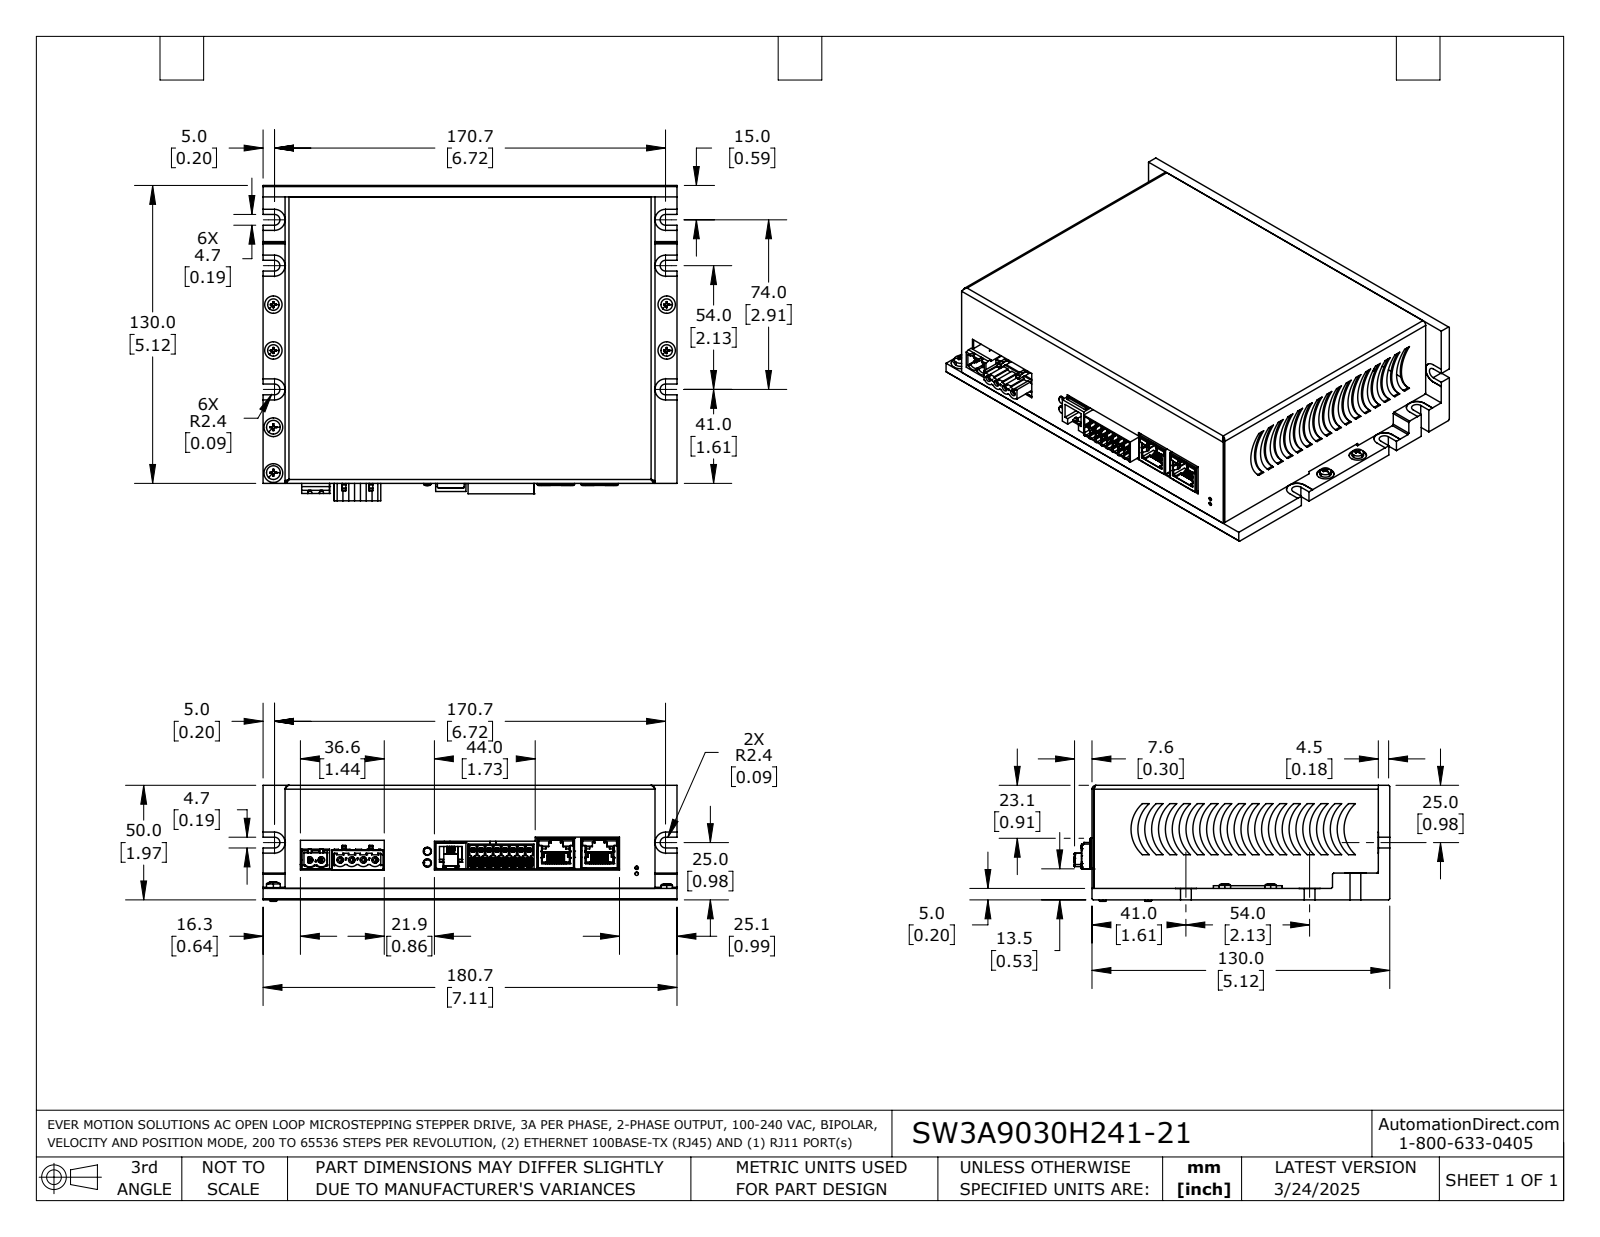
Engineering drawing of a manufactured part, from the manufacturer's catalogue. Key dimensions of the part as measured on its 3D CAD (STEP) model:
Part name (STEP PRODUCT): SW3A9030H241-21C0680
STEP written by: SolidWorks 2021 (AUTOMOTIVE_DESIGN)
Units: inches
Bodies: 21 solids, 4092 faces (2374 planar, 1426 cylindrical, 292 other)
Overall size (bounding box): 7.114 × 5.418 × 1.994
Volume: 15.08 in³ · Surface area: 310 in²
Round holes (diameter × count): ⌀0.03 ×32, ⌀0.035 ×20, ⌀0.055 ×20, ⌀0.039 ×17, ⌀0.06 ×12, ⌀0.081 ×11, ⌀0.098 ×7, ⌀0.106 ×7, ⌀0.059 ×6, ⌀0.08 ×6, ⌀0.04 ×4, ⌀0.047 ×4
Round bosses / shafts (diameter × count): ⌀0.197 ×6, ⌀0.098 ×6, ⌀0.236 ×2, ⌀0.162 ×2, ⌀0.148 ×2, ⌀0.12 ×2, ⌀0.118 ×2, ⌀0.055 ×2
Partial cylindrical surfaces — rounded edges, fillets, slot ends (radius × count): R0.004 ×144, R0.591 ×32, R0.01 ×26, R0.015 ×24, R0.006 ×20, R0.008 ×20, R0.012 ×16, R0.035 ×16
Main face-to-face distances: 0.028, 0.197, 0.47, 1.969, 1.499, 1.941, 1.471, 0.063, 0.533, 1.408
Hole centre spacings: 0.2, 0.283, 0.4, 0.1, 0.447, 0.787, 1.244, 0.6
